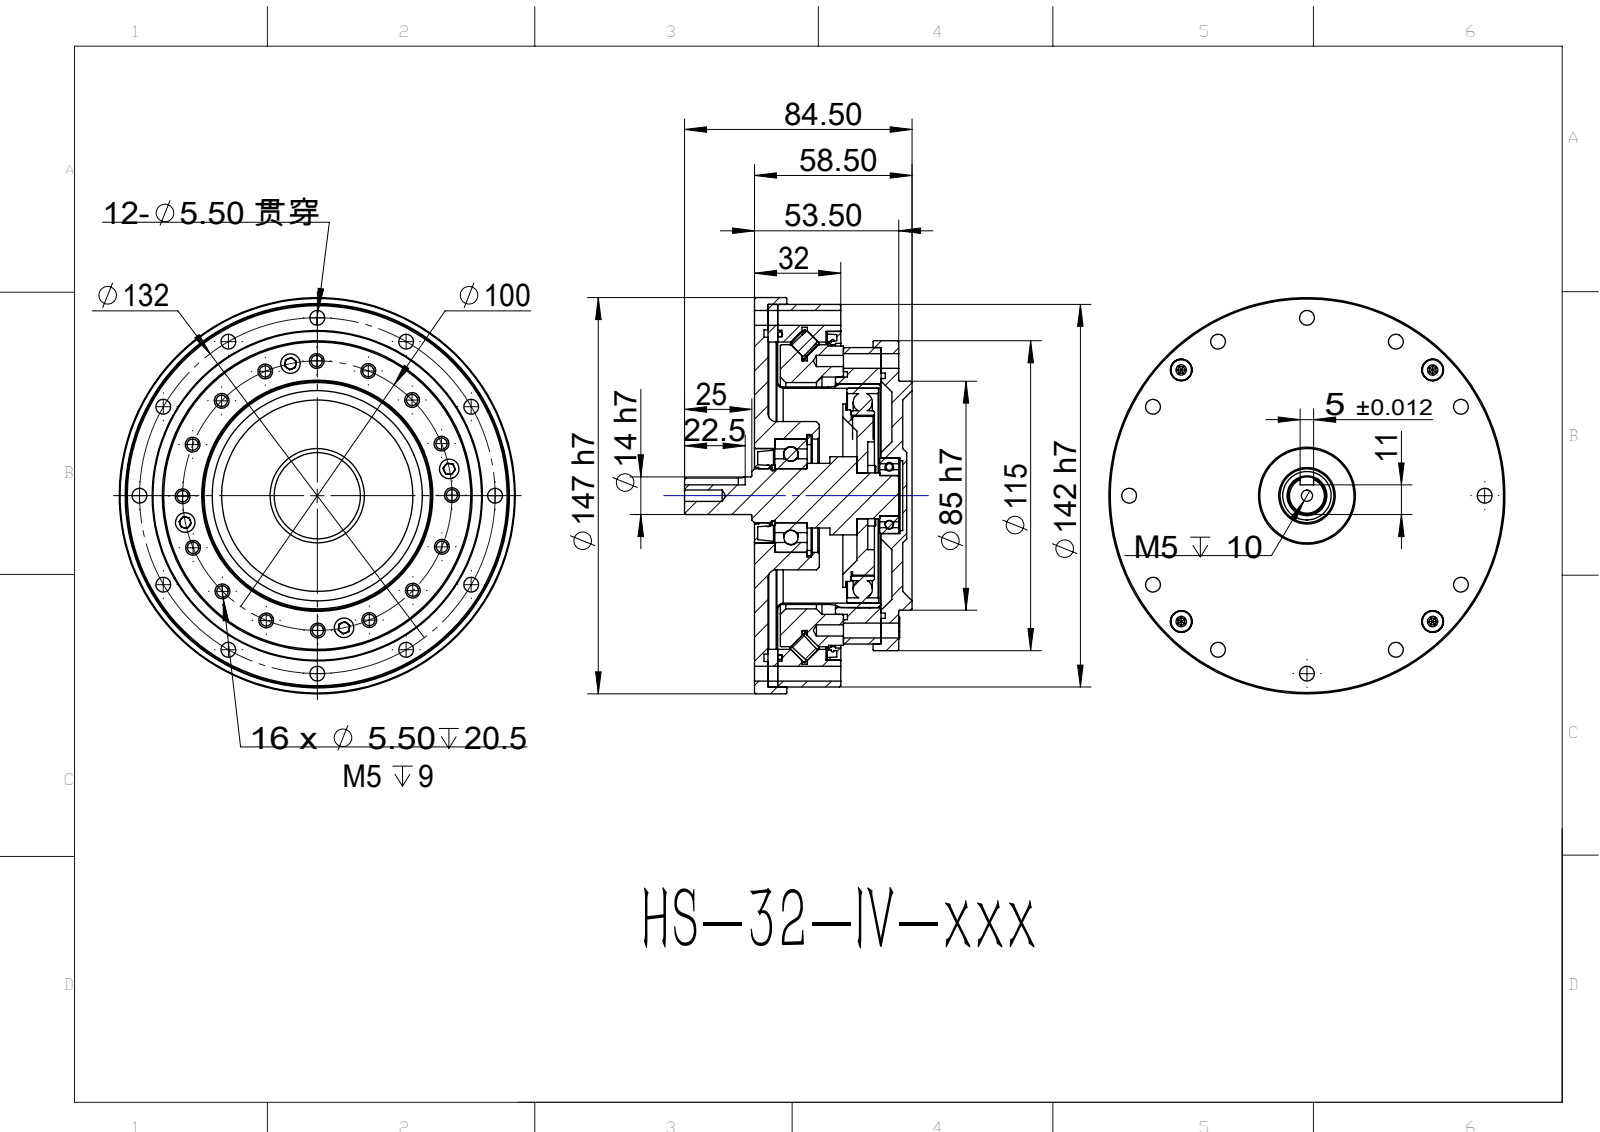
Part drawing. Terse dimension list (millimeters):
name: HS-32-IV; ????-STXB-32080-01; ????35??20?7; deep groove ball bearings gb_Rolling bearings 61902 GB 276-94 (+8 more)
written by: ONSHAPE BY PTC INC, 1.201 (AP242_MANAGED_MODEL_BASED_3D_ENGINEERING_MIM_LF)
unit: mm
bodies: 106 solids, 1455 faces (734 planar, 372 cylindrical, 349 other)
size: 147 × 147 × 84.5
volume: 531 674 mm³; area: 290 966 mm²
holes: 28× ⌀5.5, 17× ⌀4.2, 12× ⌀3.3, 8× ⌀4.5, 8× ⌀8, 5× ⌀2.5, 4× ⌀3.5, 2× ⌀2, 2× ⌀3, 1× ⌀3.4, 1× ⌀6, 1× ⌀15
bosses: 36× ⌀8, 8× ⌀4, 5× ⌀5.5, 5× ⌀3, 4× ⌀8.5, 4× ⌀7, 4× ⌀5, 1× ⌀147
rounds: 36× R4, 36× R4.03, 4× R1.5, 2× R0.5, 2× R1, 2× R3, 1× R2.5, 1× R11.25
face distances: 5, 8.6, 3.6, 6.5, 4, 1, 23.4, 33, 42, 2.5
hole spacings: 70.71, 38.27, 50, 29.03, 99.52, 9.8, 19.51, 47.14
